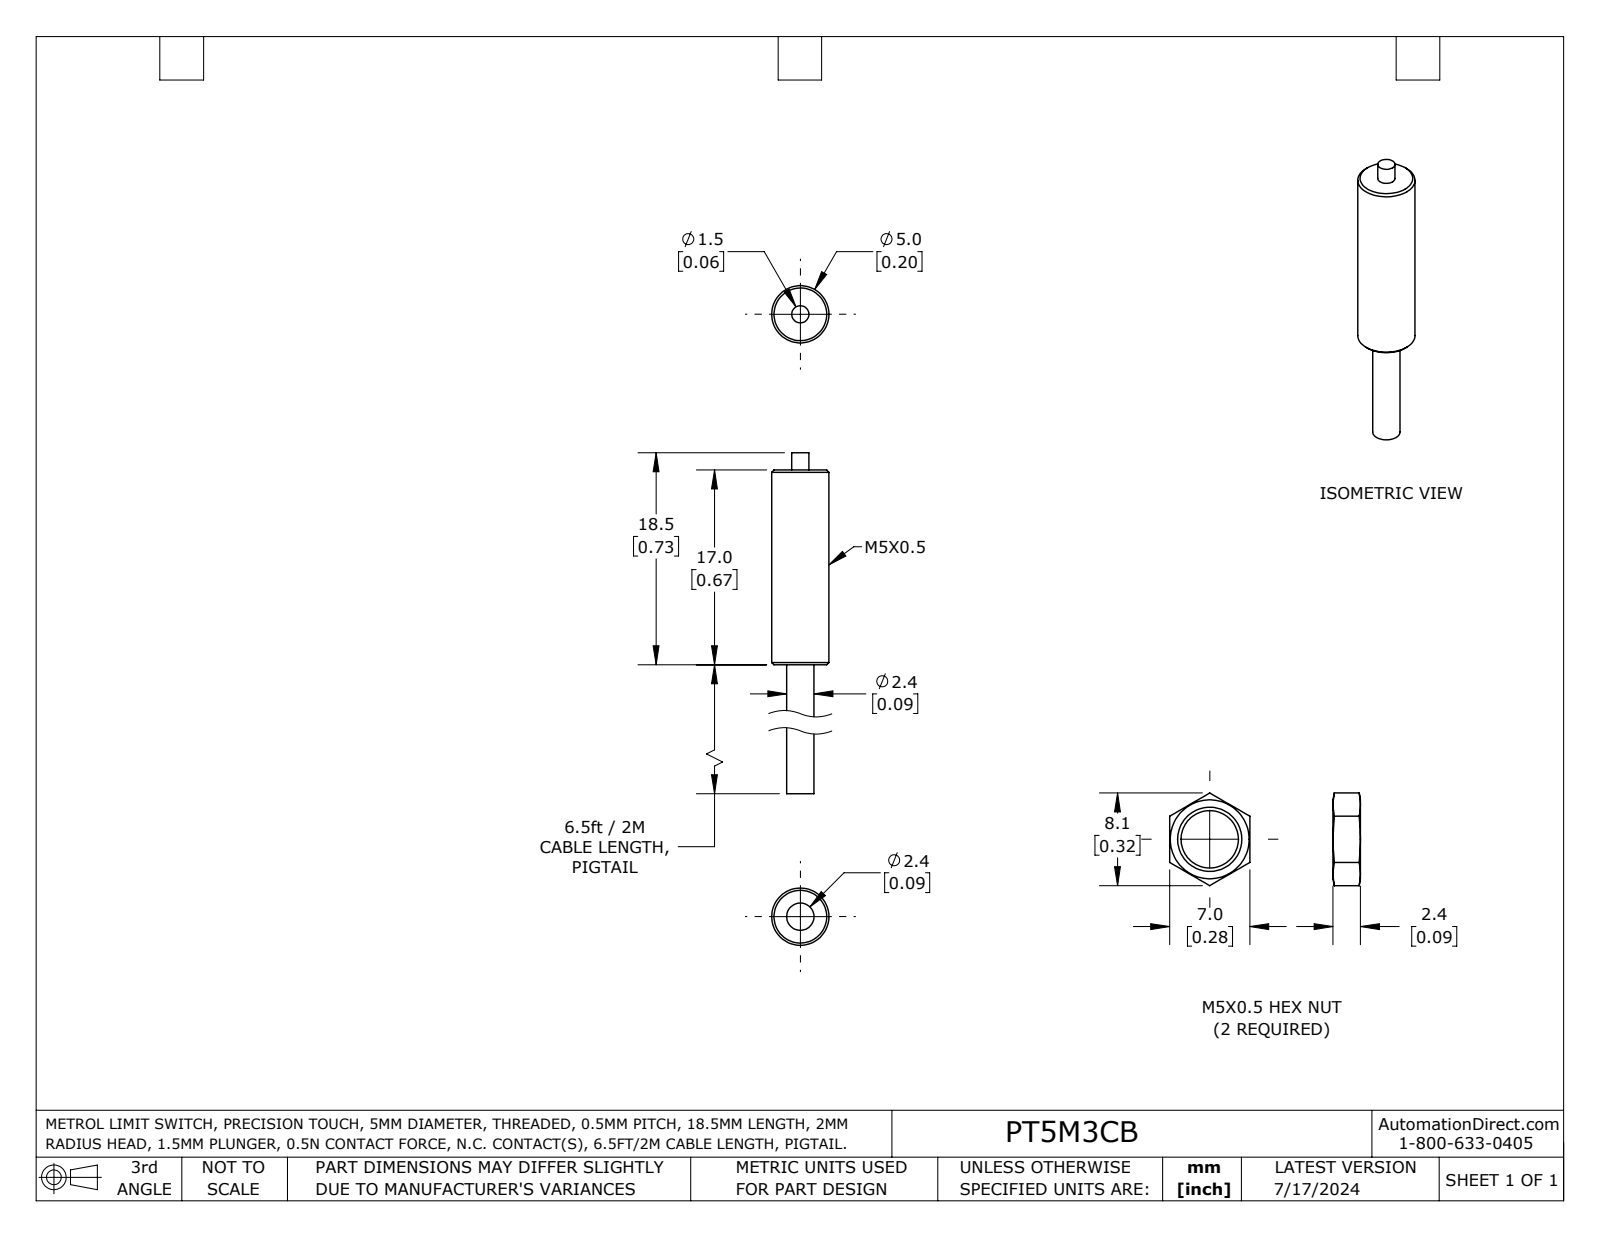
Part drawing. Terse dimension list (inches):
name: PT5M3CB
written by: SolidWorks 2023 (AUTOMOTIVE_DESIGN)
unit: in
bodies: 1 solid, 9 faces (4 planar, 3 cylindrical, 2 other)
size: 1.126 × 0.197 × 0.197
volume: 0.023 in³; area: 0.597 in²
bosses: 1× ⌀0.197, 1× ⌀0.094, 1× ⌀0.059
face distances: 0.669, 0.398, 1.067, 1.126, 0.728, 0.059
